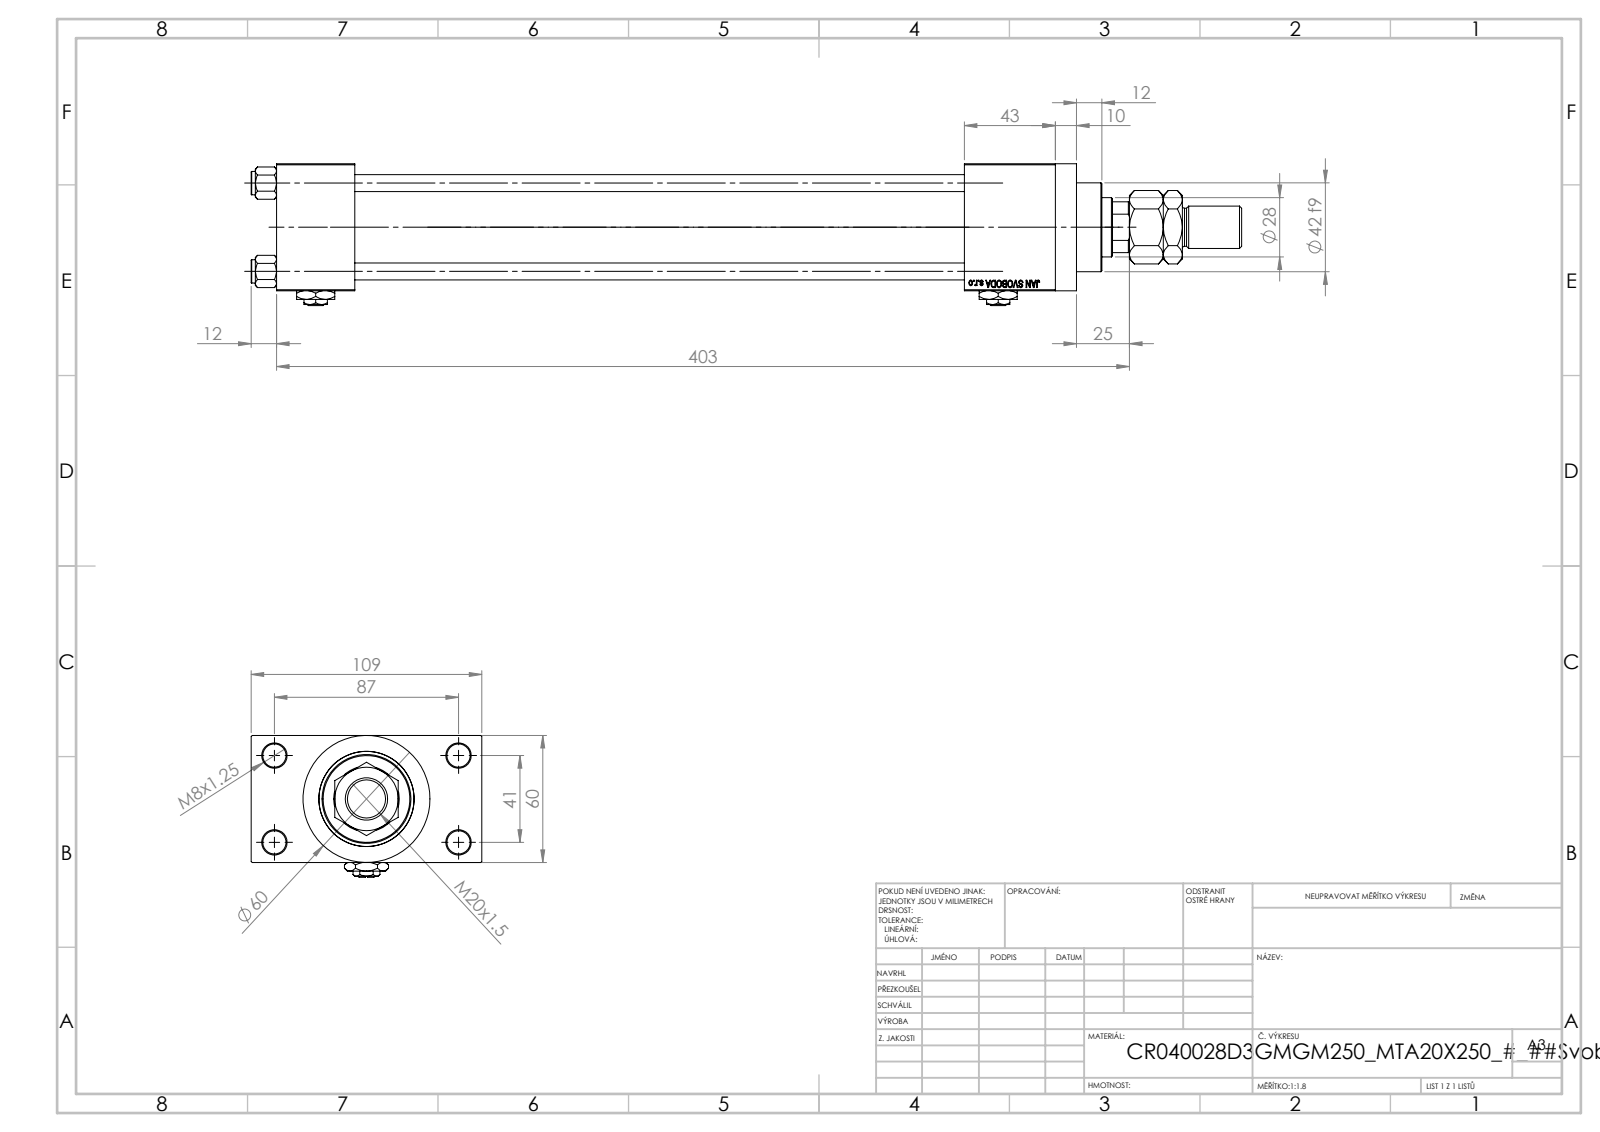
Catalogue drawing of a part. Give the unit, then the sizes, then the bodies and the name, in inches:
Units: inches
Overall size (bounding box): 18.425 × 4.291 × 2.638
Round holes (diameter × count): ⌀0.315 ×4, ⌀0.433 ×4, ⌀0.656 ×4, ⌀0.945 ×4, ⌀0.276 ×3, ⌀0.728 ×1, ⌀1.102 ×1, ⌀1.22 ×1, ⌀1.575 ×1, ⌀1.772 ×1
Round bosses / shafts (diameter × count): ⌀0.433 ×4, ⌀2.362 ×1, ⌀1.811 ×1, ⌀1.654 ×1, ⌀0.787 ×1, ⌀0.709 ×1
Partial cylindrical surfaces — rounded edges, fillets, slot ends (radius × count): R0.531 ×1
Main face-to-face distances: 2.362, 0.965, 11.339, 3.327, 1.457, 12.795, 14.488, 13.031, 1.693, 4.291
Hole centre spacings: 0.892, 1.161, 1.642, 1.856, 1.893, 2.533, 3.011, 1.614
Volume: 51.02 in³ · Surface area: 376.7 in²
Bodies: 14 solids, 1254 faces (561 planar, 103 cylindrical, 590 other)
Part name (STEP PRODUCT): Zatka_pro_OIL_PORT; V215CR_D_Body; V215_VC_A; V215CR_VCP_D (+3 more)
STEP written by: SolidWorks 2019 (CONFIG_CONTROL_DESIGN)
